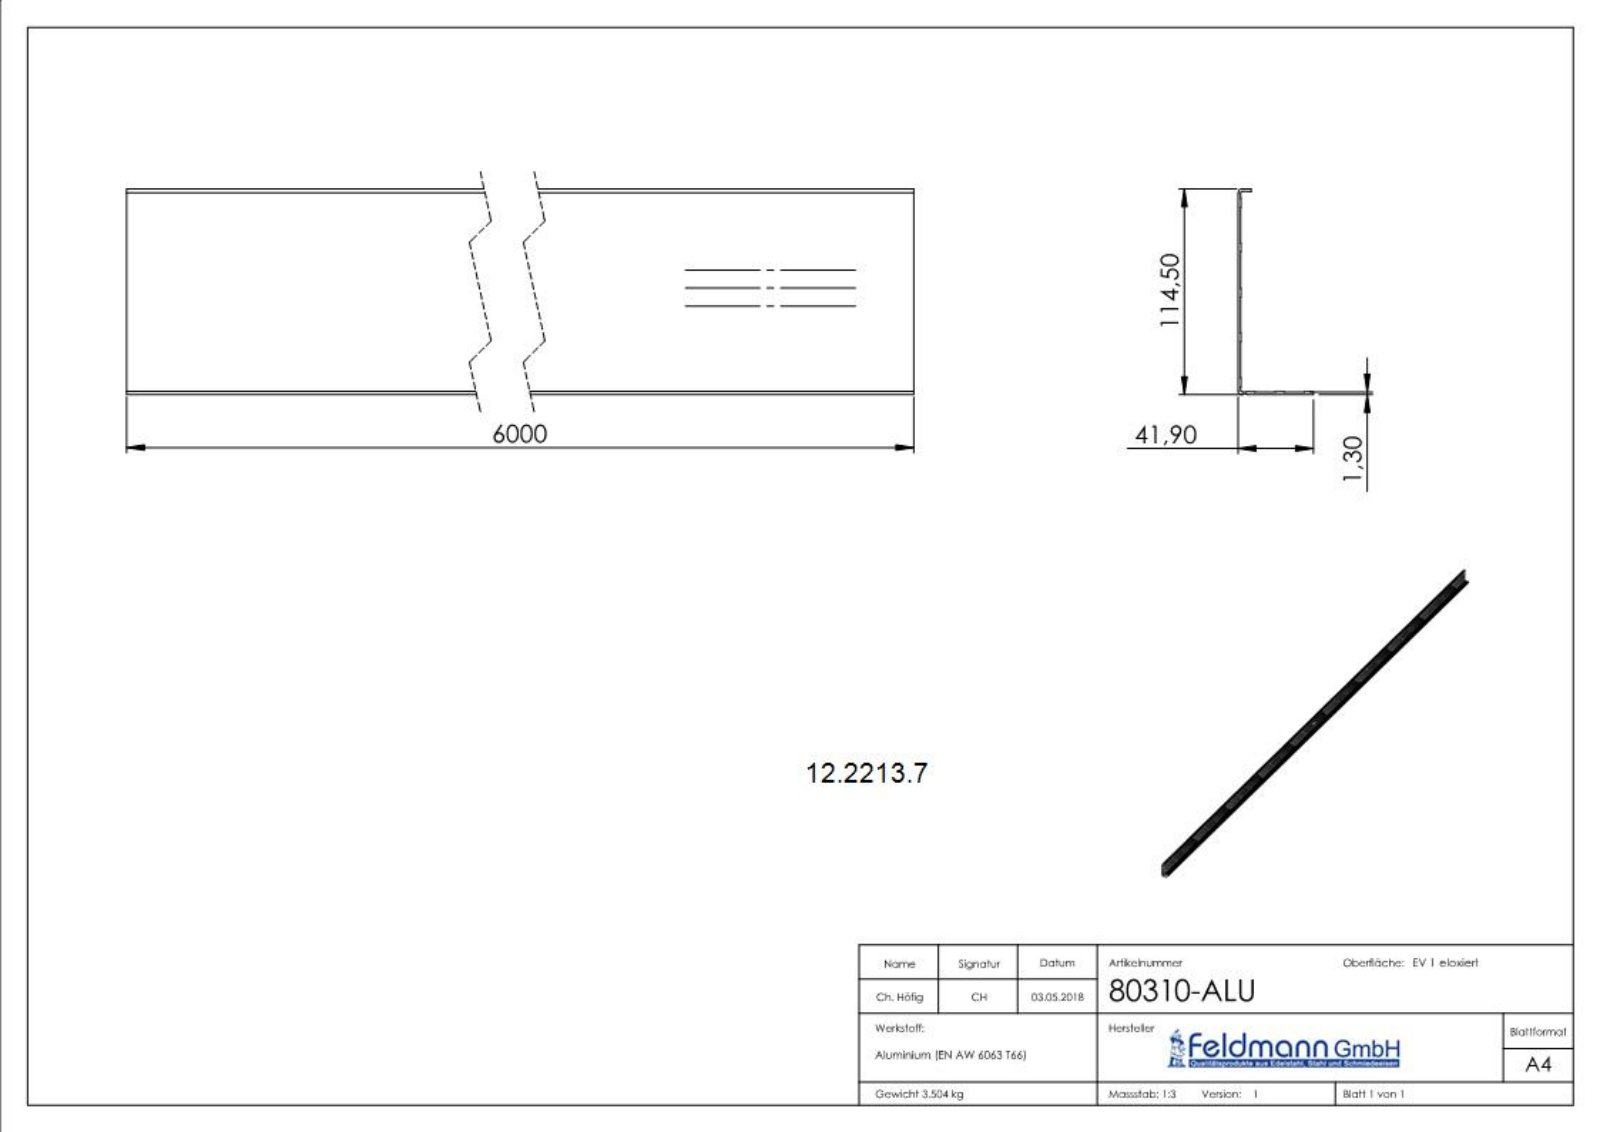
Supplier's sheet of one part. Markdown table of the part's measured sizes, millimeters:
| quantity | value |
| --- | --- |
| part name | 80310-ALU |
| STEP written by | SolidWorks 2015 (CONFIG_CONTROL_DESIGN) |
| units | millimeters |
| bodies | 1 solid, 267 faces (156 planar, 7 cylindrical, 104 other) |
| overall size | 6000 × 114.5 × 41.9 |
| volume | 1 298 000 mm³ |
| surface area | 1 953 000 mm² |
| partial cylindrical surfaces (radius × count) | 0.3 × 2, 1.2 × 2, 1.7 × 1, 2 × 1, 2.2 × 1 |
| main face-to-face distances | 1.3, 1.5, 114.5, 113.2, 113, 25, 5, 7.2, 5.9, 5.7 |
